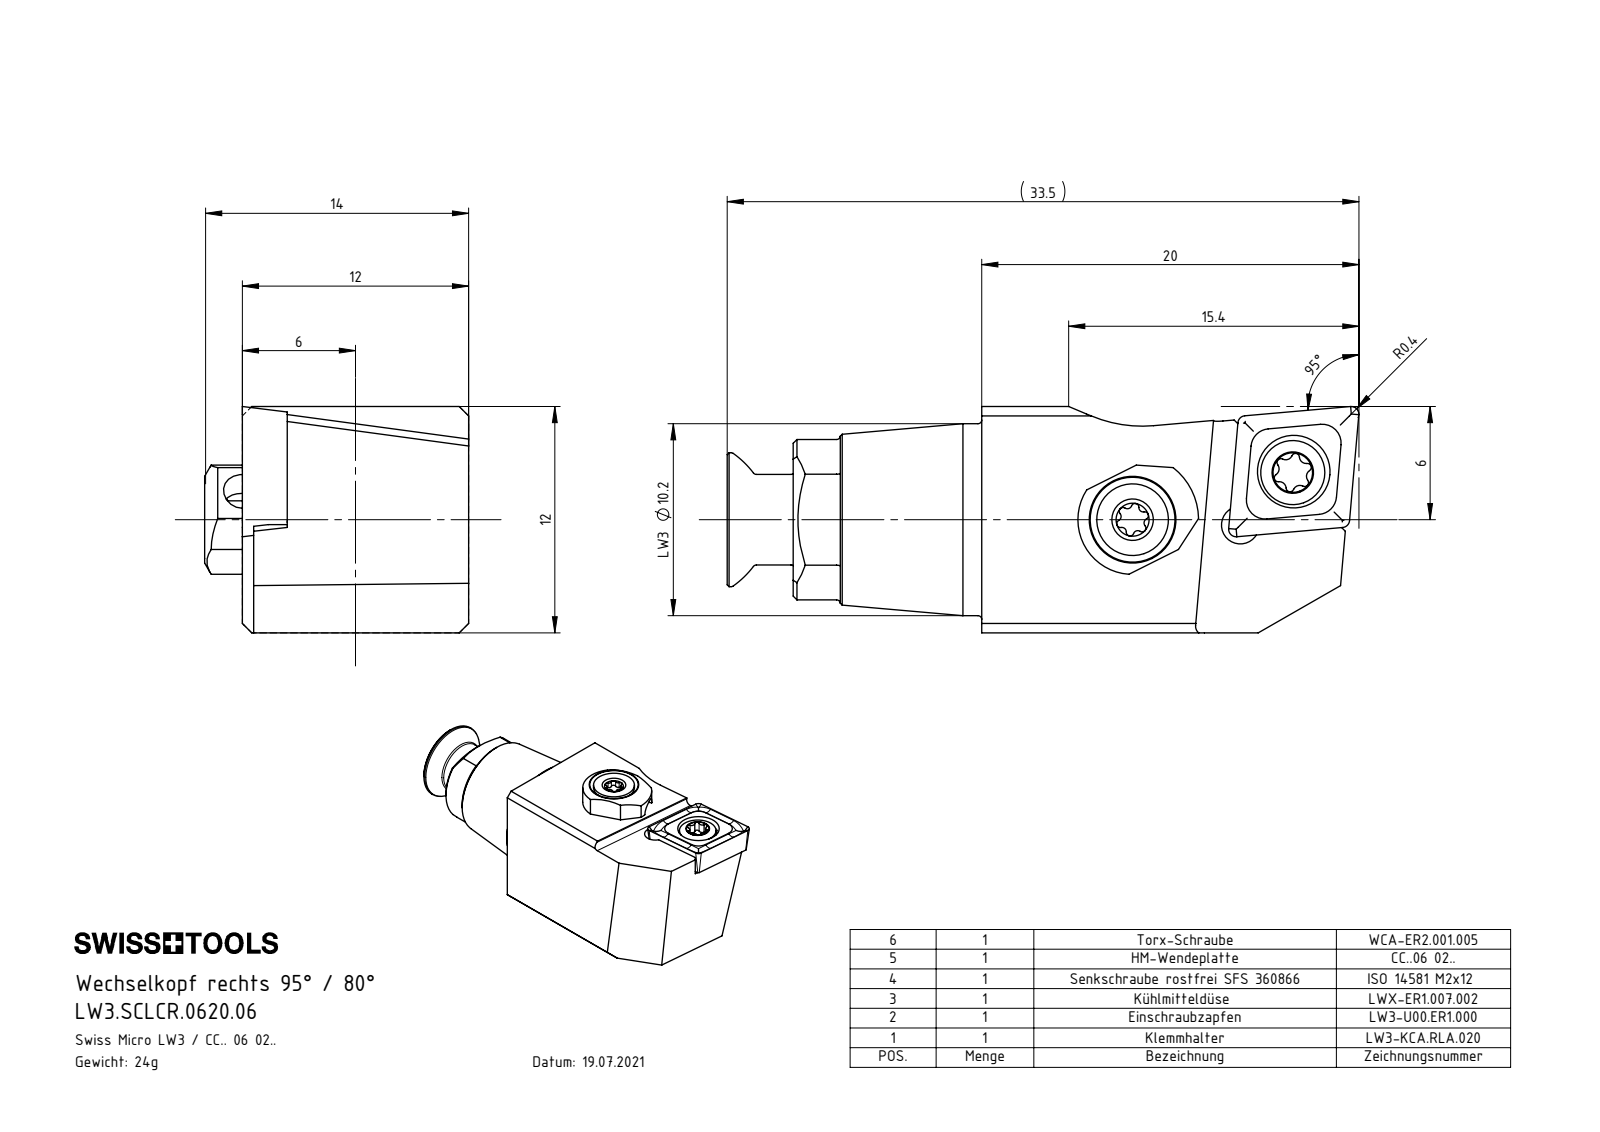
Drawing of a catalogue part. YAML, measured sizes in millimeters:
part_name: "WCA-ER2.001.005_A; LW3.SCLCR.0620.06; ISO 14581 - M2x12; LW3-U00.ER1.000_B (+3 more)"
step_written_by: "SolidWorks 2017 (CONFIG_CONTROL_DESIGN)"
units: millimeters
bodies: {solids: 6, faces: 186, planar: 69, cylindrical: 52, other: 65}
overall_size: [33.4, 14, 12]
volume: 3025
surface_area: 2389
round_holes:
  - {diameter: 2, count: 2}
  - {diameter: 1.6, count: 1}
  - {diameter: 2.05, count: 1}
  - {diameter: 2.5, count: 1}
  - {diameter: 2.8, count: 1}
  - {diameter: 3, count: 1}
  - {diameter: 3.85, count: 1}
  - {diameter: 5.5, count: 1}
round_bosses_or_shafts:
  - {diameter: 10.18, count: 1}
  - {diameter: 6.9, count: 1}
  - {diameter: 6, count: 1}
  - {diameter: 5, count: 1}
  - {diameter: 4.8, count: 1}
  - {diameter: 3.8, count: 1}
  - {diameter: 3.4, count: 1}
  - {diameter: 2.5, count: 1}
partial_cylinders:
  - {radius: 0.2, count: 8}
  - {radius: 0.21, count: 6}
  - {radius: 0.24, count: 6}
  - {radius: 0.36, count: 5}
  - {radius: 0.36, count: 1}
  - {radius: 0.5, count: 1}
  - {radius: 1, count: 1}
  - {radius: 2.9, count: 1}
face_to_face_distances: [12, 11.4, 9.62, 2.38, 1.78, 0.6, 2, 2.5, 13.4, 7]
hole_center_spacings: [3.95, 4.02, 5.72, 8.86, 8.92]
